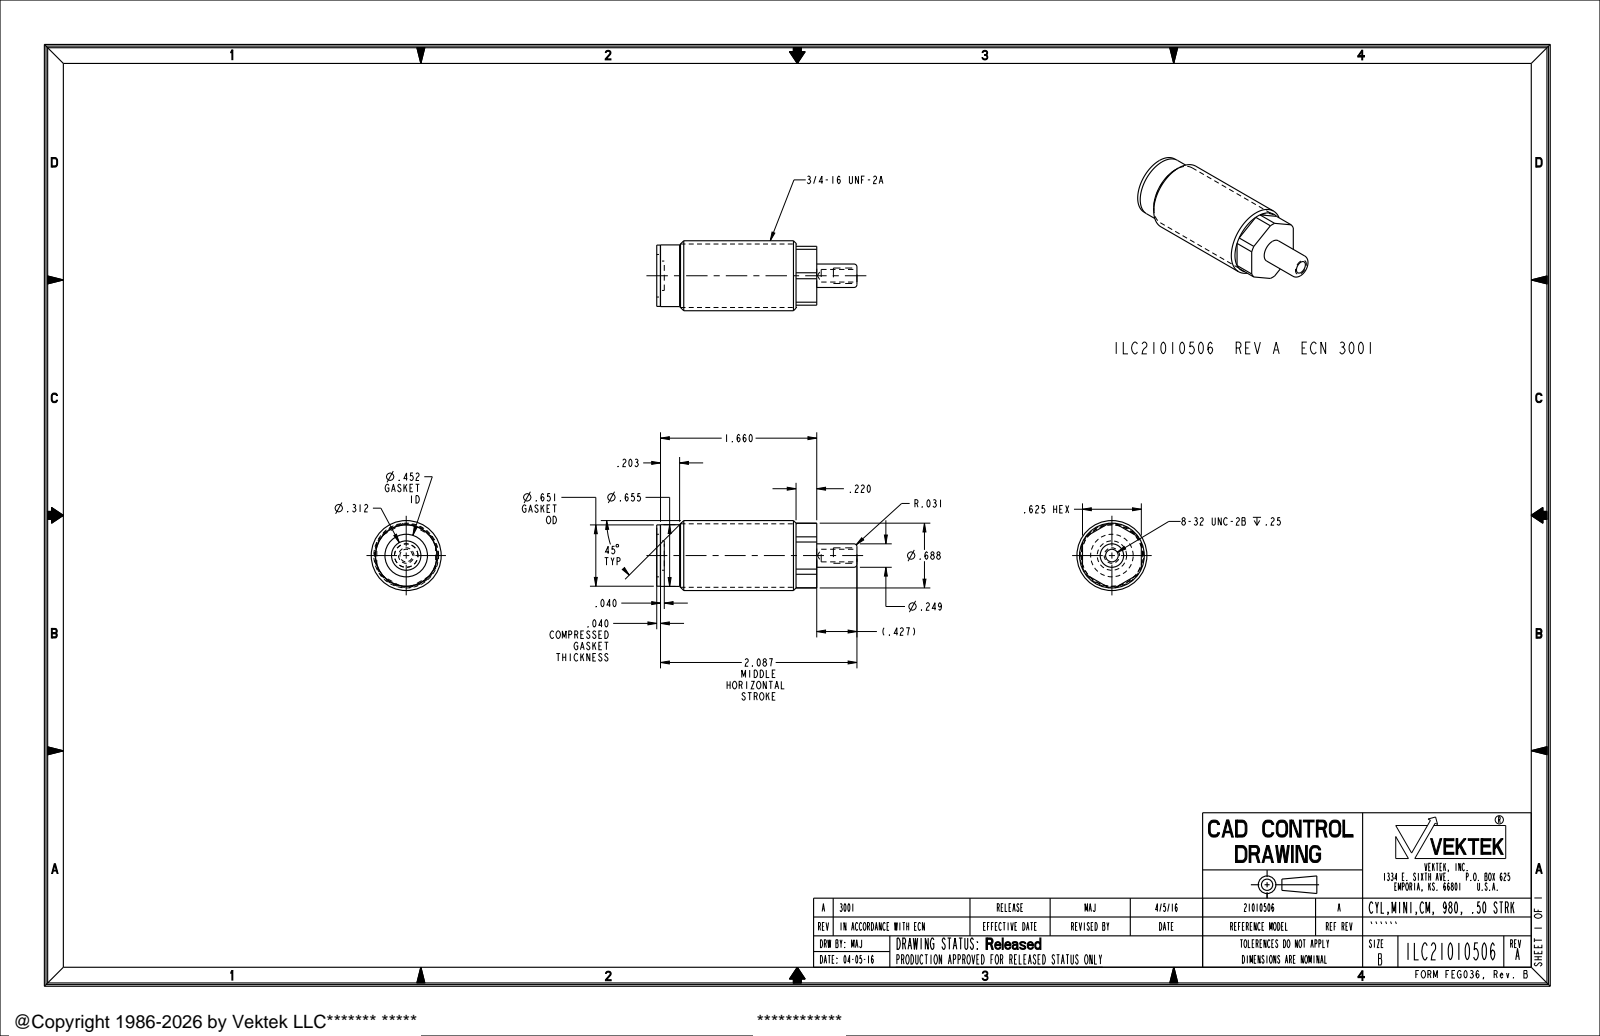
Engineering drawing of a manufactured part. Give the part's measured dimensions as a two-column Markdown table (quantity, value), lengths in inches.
| quantity | value |
| --- | --- |
| part name | ILC21010506 |
| STEP written by | PRO/ENGINEER BY PARAMETRIC TECHNOLOGY CORPORATION, 2013320 (AUTOMOTIVE_DESIGN) |
| units | inches |
| bodies | 2 solids, 52 faces (20 planar, 24 cylindrical, 8 other) |
| overall size | 2.127 × 0.743 × 0.743 |
| volume | 0.694 in³ |
| surface area | 8.631 in² |
| round holes (diameter × count) | 0.134 × 1, 0.312 × 1, 0.452 × 1 |
| round bosses / shafts (diameter × count) | 0.743 × 1, 0.674 × 1, 0.655 × 1, 0.651 × 1, 0.249 × 1, 0.164 × 1 |
| partial cylindrical surfaces (radius × count) | 0.344 × 1 |
| main face-to-face distances | 0.22, 1.44, 1.66, 0.04, 0.625, 0.039, 1.48, 1.7, 1.441, 1.661 |
